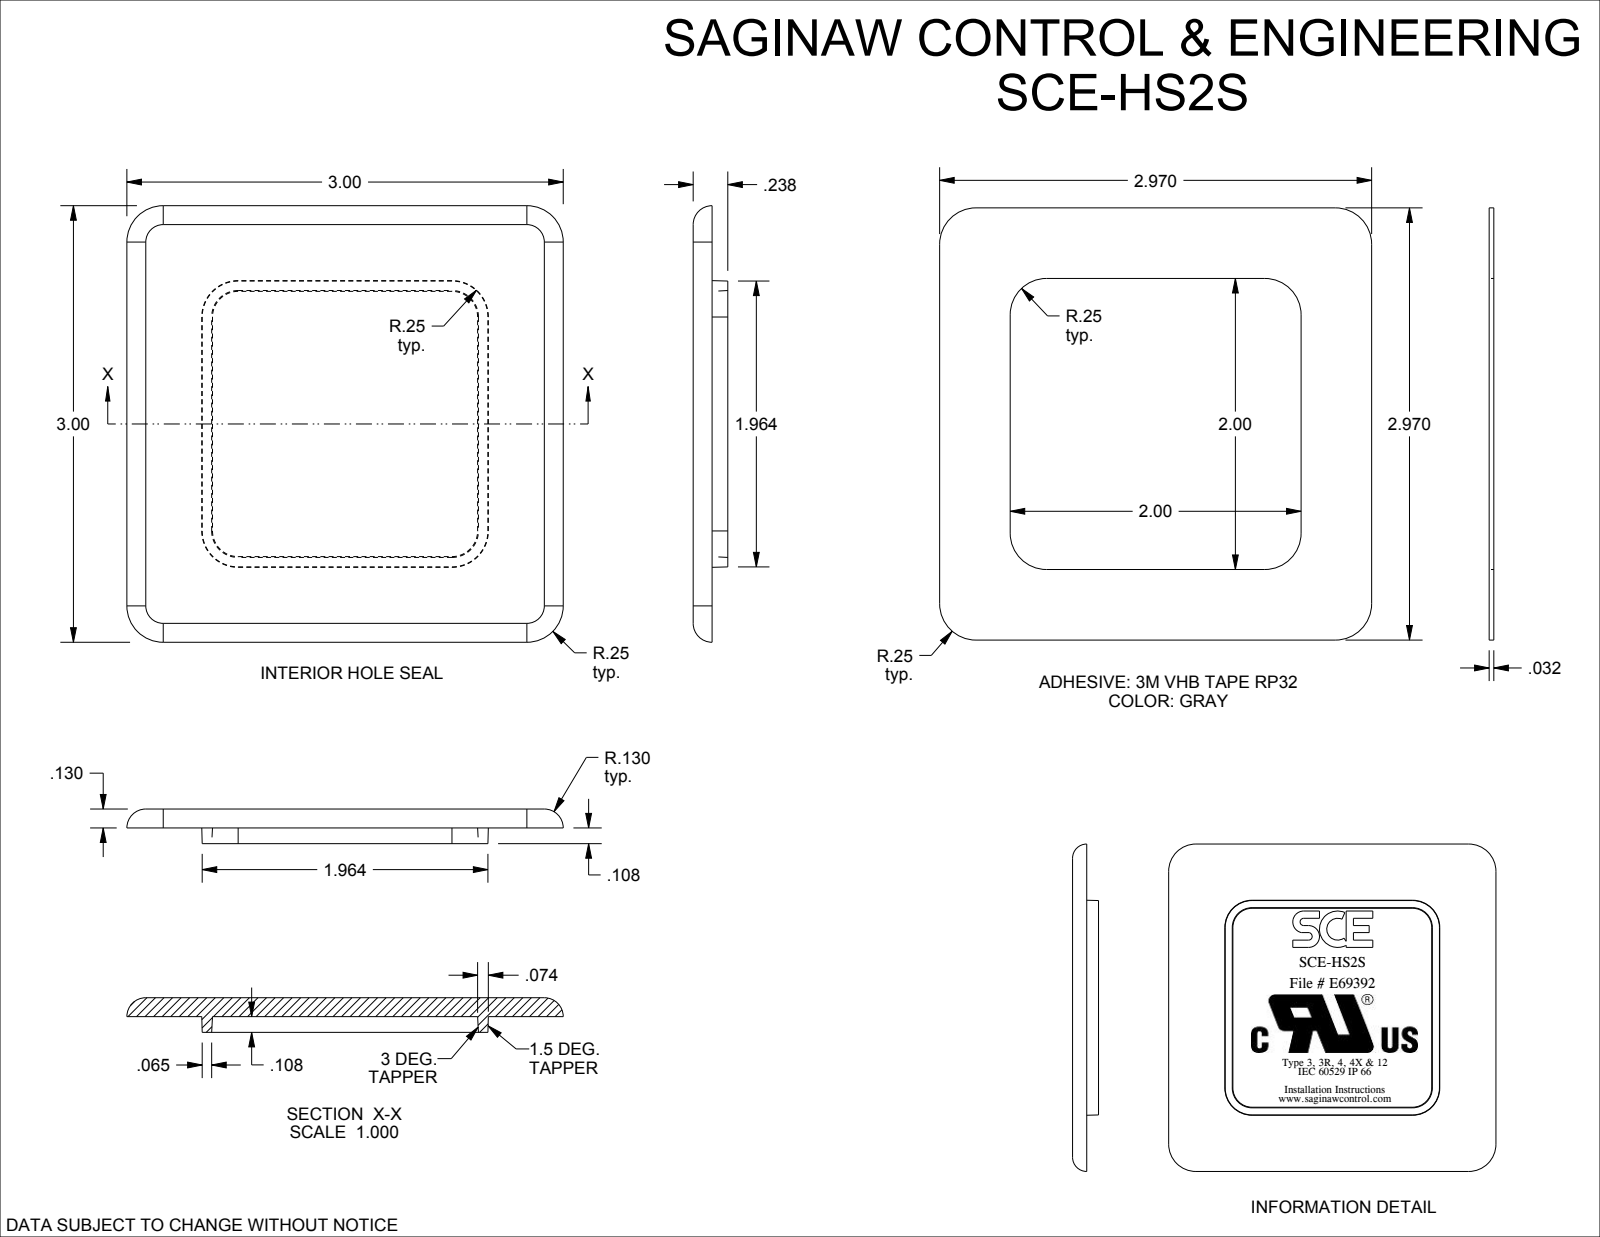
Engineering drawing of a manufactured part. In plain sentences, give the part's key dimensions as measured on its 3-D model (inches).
The part is named "SCE-HS2S". Its 3-D file was written by "SolidWorks 2019 (AUTOMOTIVE_DESIGN)". It is 2 solids with 46 faces: 22 planar, 12 cylindrical and 12 other. Overall it measures 3 by 3 by 0.238 inches. Its volume is 1.33 cubic inches and its surface area 30.5 square inches. Partial cylindrical surfaces (rounded edges, fillets, slot ends): 8 of radius 0.25, 4 of radius 0.13. The main face-to-face distances are 0.13, 0.032, 0.162, 0.076, 0.108, 0.238, 0.485, 2.485, 2.97, 2.
